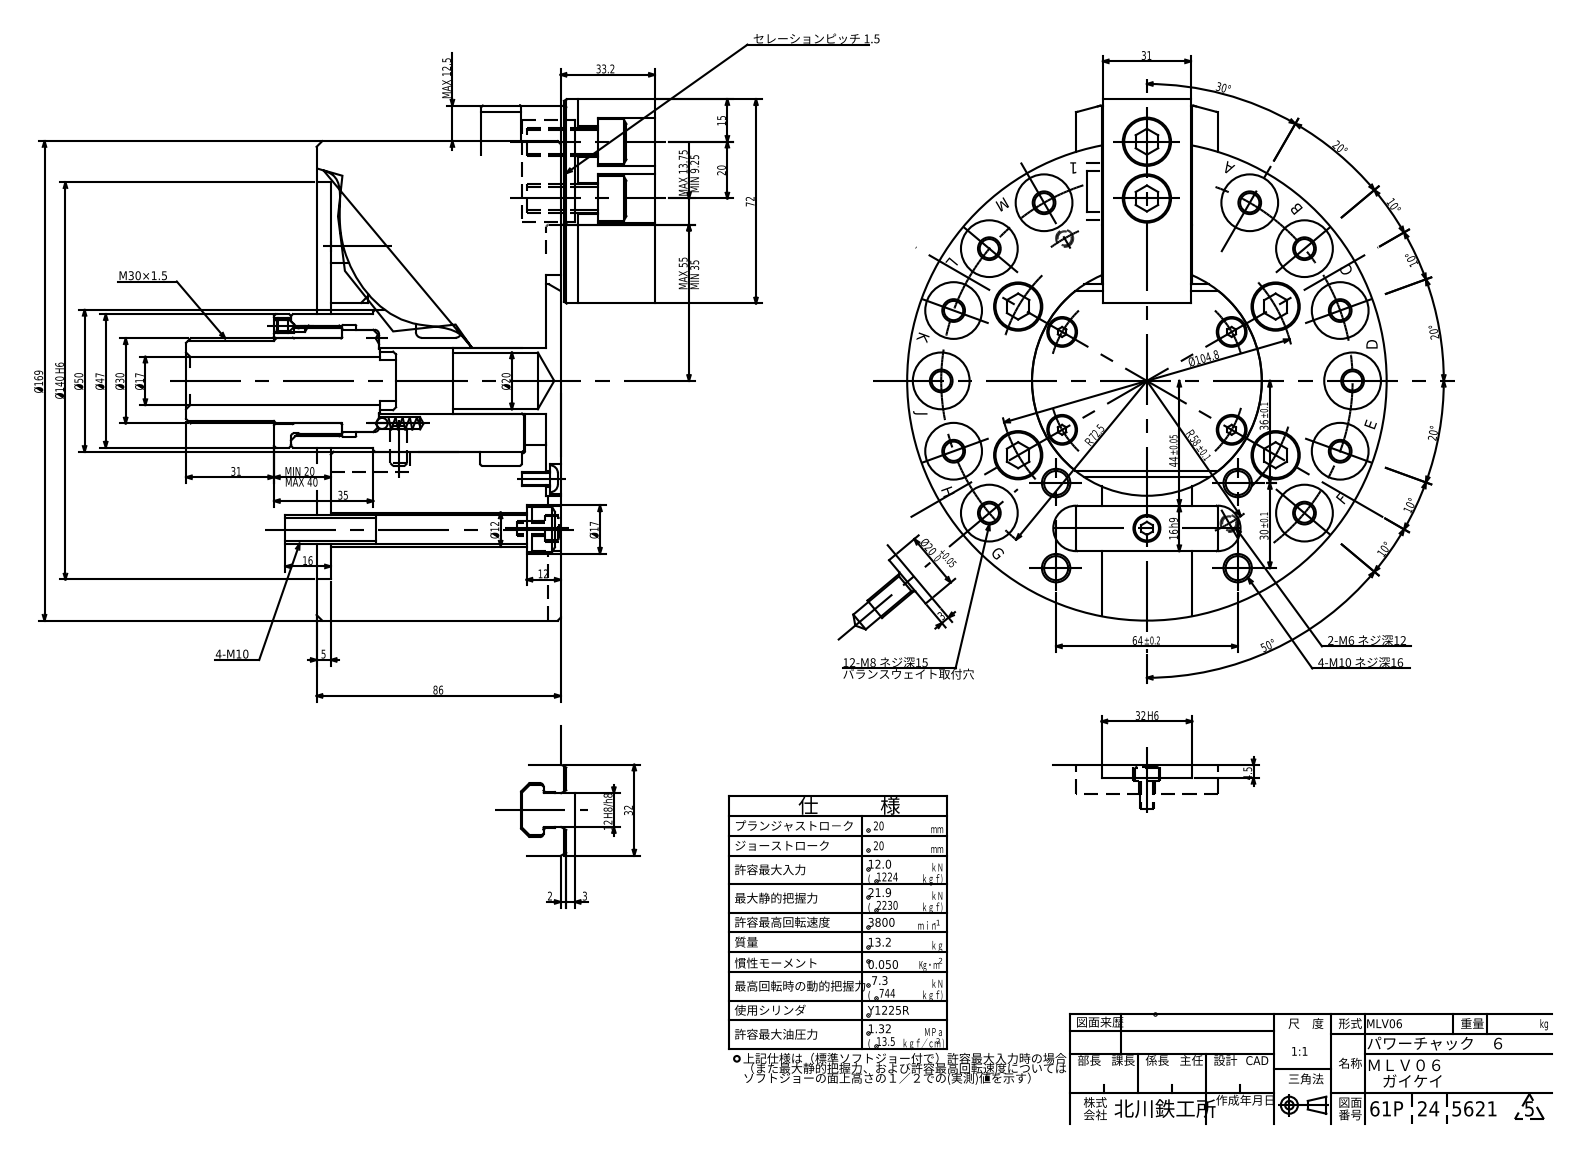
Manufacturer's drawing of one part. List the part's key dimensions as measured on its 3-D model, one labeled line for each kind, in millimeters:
Part name (STEP PRODUCT): 61P245481_MLV06_ASSY
STEP written by: ST-DEVELOPER v16.7 (AUTOMOTIVE_DESIGN)
Units: millimetres
Bodies: 21 solids, 1211 faces (876 planar, 210 cylindrical, 125 other)
Overall size (bounding box): 188.29 × 169 × 165.2
Volume: 1 766 000 mm³ · Surface area: 262 386 mm²
Round holes (diameter × count): ⌀5 ×15, ⌀6.8 ×13, ⌀8 ×13, ⌀20 ×12, ⌀4.2 ×7, ⌀6 ×7, ⌀17 ×7, ⌀5.5 ×5, ⌀11 ×5, ⌀8.5 ×4, ⌀10 ×4, ⌀10.5 ×4
Round bosses / shafts (diameter × count): ⌀9.5 ×4, ⌀10 ×3, ⌀16 ×2, ⌀169 ×1, ⌀81 ×1, ⌀47 ×1, ⌀37 ×1, ⌀30 ×1
Partial cylindrical surfaces — rounded edges, fillets, slot ends (radius × count): R2.1 ×6, R6 ×6, R5 ×4, R8 ×4, R0.3 ×2, R1 ×2, R2 ×2, R7 ×2
Main face-to-face distances: 5, 81.3, 81, 3, 14, 76.3, 4.7, 9, 28, 86
Hole centre spacings: 72.5, 142.8, 38.99, 106.65, 136.26, 22.8, 25.18, 34.5
